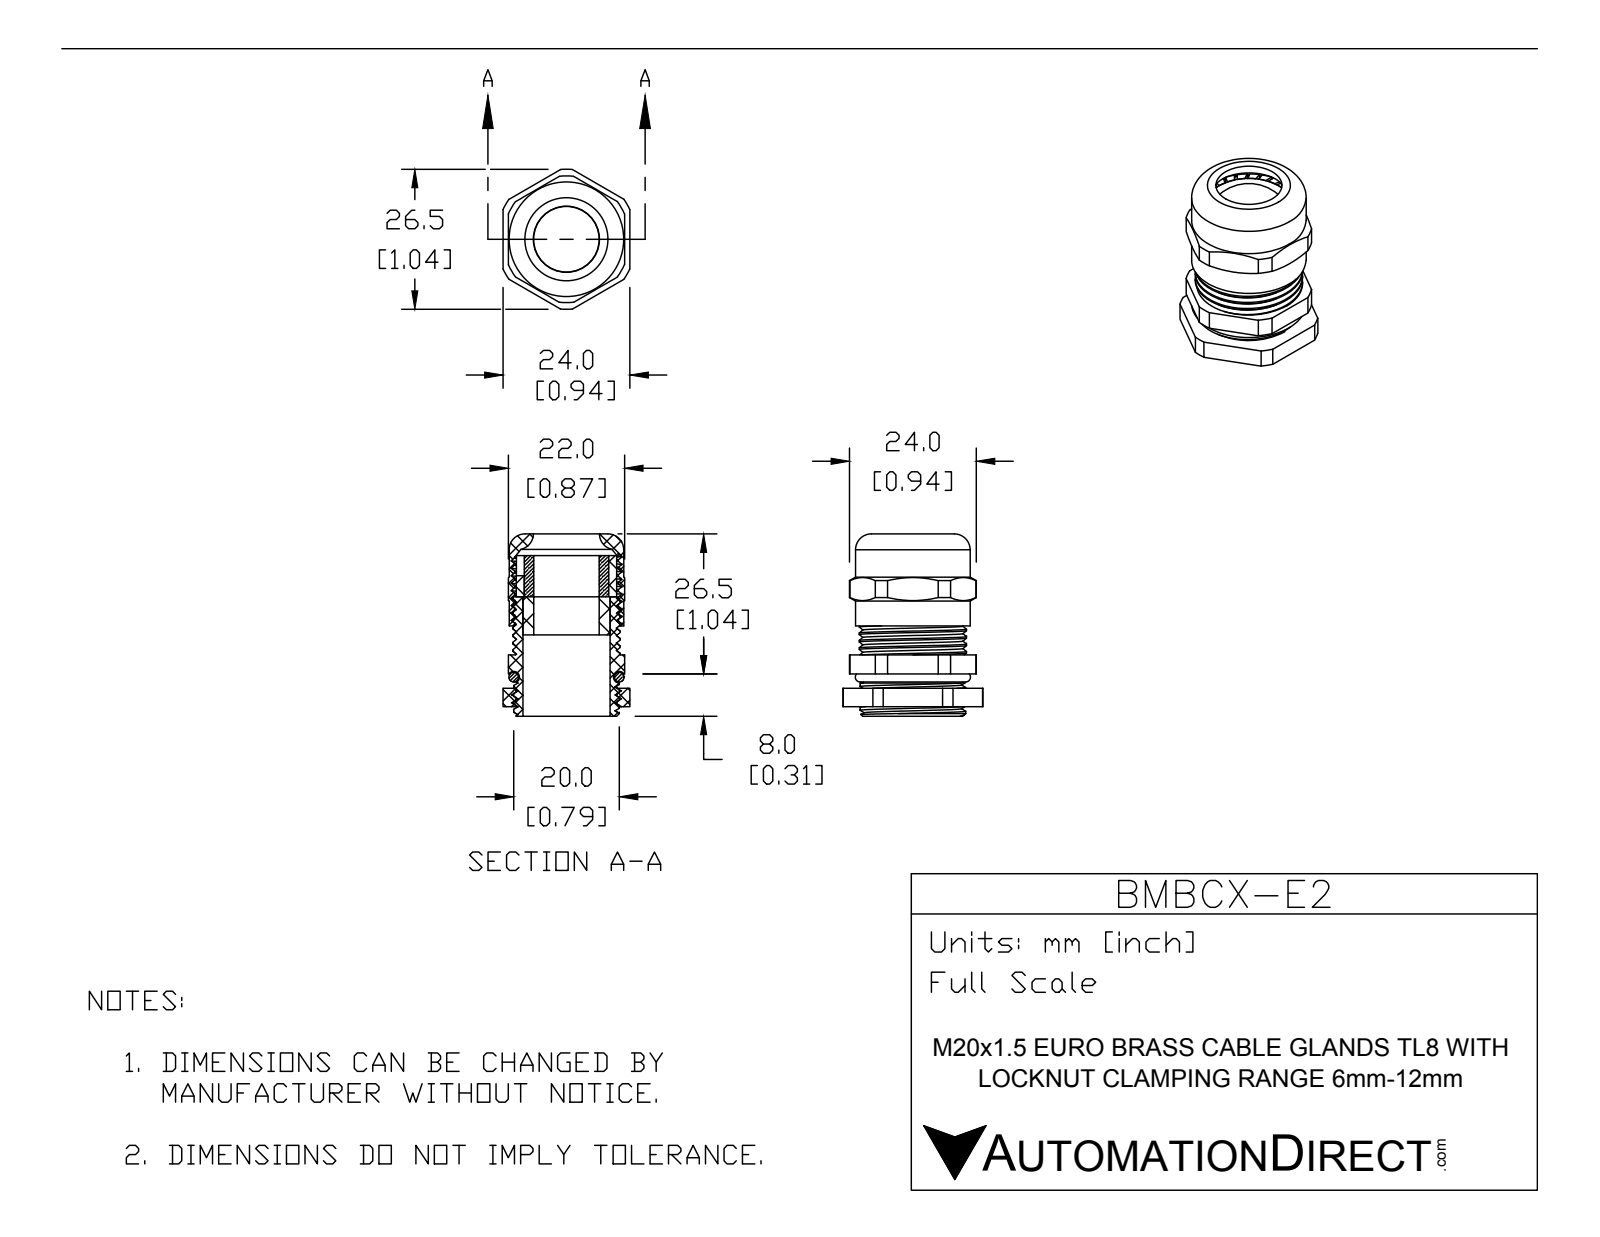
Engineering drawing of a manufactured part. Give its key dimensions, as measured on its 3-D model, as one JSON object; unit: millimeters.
{"part_name": "BMBCX-E2", "step_written_by": "SolidWorks 2015 (CONFIG_CONTROL_DESIGN)", "units": "millimeters", "bodies": {"solids": 6, "faces": 254, "planar": 133, "cylindrical": 90, "other": 31}, "overall_size": [34.5, 26.5, 24], "volume_mm3": 6500, "surface_area_mm2": 10878, "round_holes": [[12.4, 1], [16, 1], [16.5, 1], [19.19, 1], [19.63, 1]], "round_bosses_or_shafts": [[21.7, 1], [20.3, 1], [20, 1], [19, 1]], "partial_cylinders_radius": [[12, 1], [13.25, 1]], "face_to_face_distances": [1, 23, 22, 17.3, 3.5, 20.8, 28.6, 25.1, 7.8, 0.5]}
